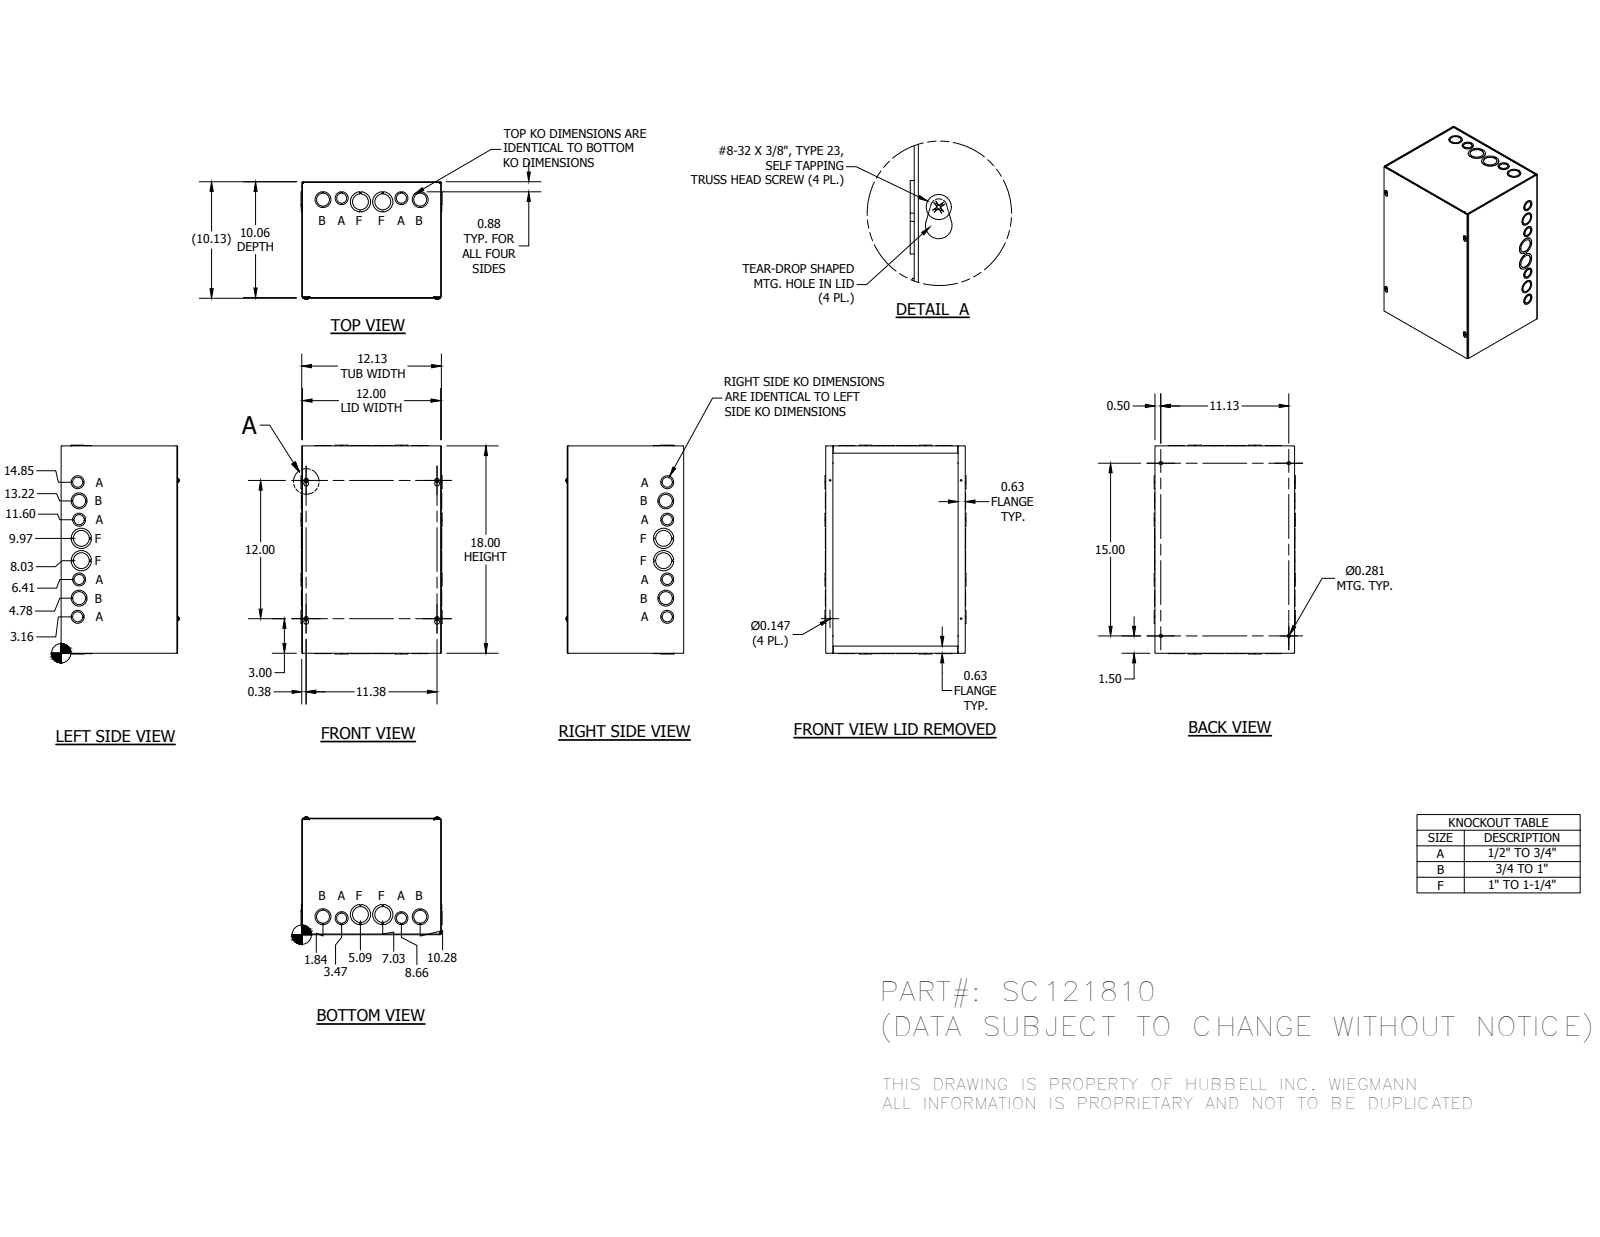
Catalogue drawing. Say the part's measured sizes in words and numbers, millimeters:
The part is named "SC121810BLR; SC1210TB; SC1218LPA; 34056 (+1 more)". Its 3-D file was written by "Autodesk Inventor 2014 (AUTOMOTIVE_DESIGN)". It is 29 solids with 1055 faces: 771 planar, 216 cylindrical and 68 other. Overall it measures 460.38 by 311.15 by 259.72 millimeters. Round holes: 12 of diameter 28.57, 8 of diameter 22.22, 8 of diameter 34.92, 4 of diameter 3.73, 4 of diameter 7.14, 4 of diameter 44.45. Round bosses or shafts: 4 of diameter 9.75, 4 of diameter 4.17. Partial cylindrical surfaces (rounded edges, fillets, slot ends): 12 of radius 0.79, 12 of radius 2.38, 4 of radius 3.17, 4 of radius 5.16. The main face-to-face distances are 1.59, 306.39, 254, 1.58, 455.61, 255.58, 255.59, 257.17, 304.8, 307.98. The hole center spacings are 38.23, 41.4, 42.03, 82.69, 90.9, 131.92, 173.13, 288.28.
